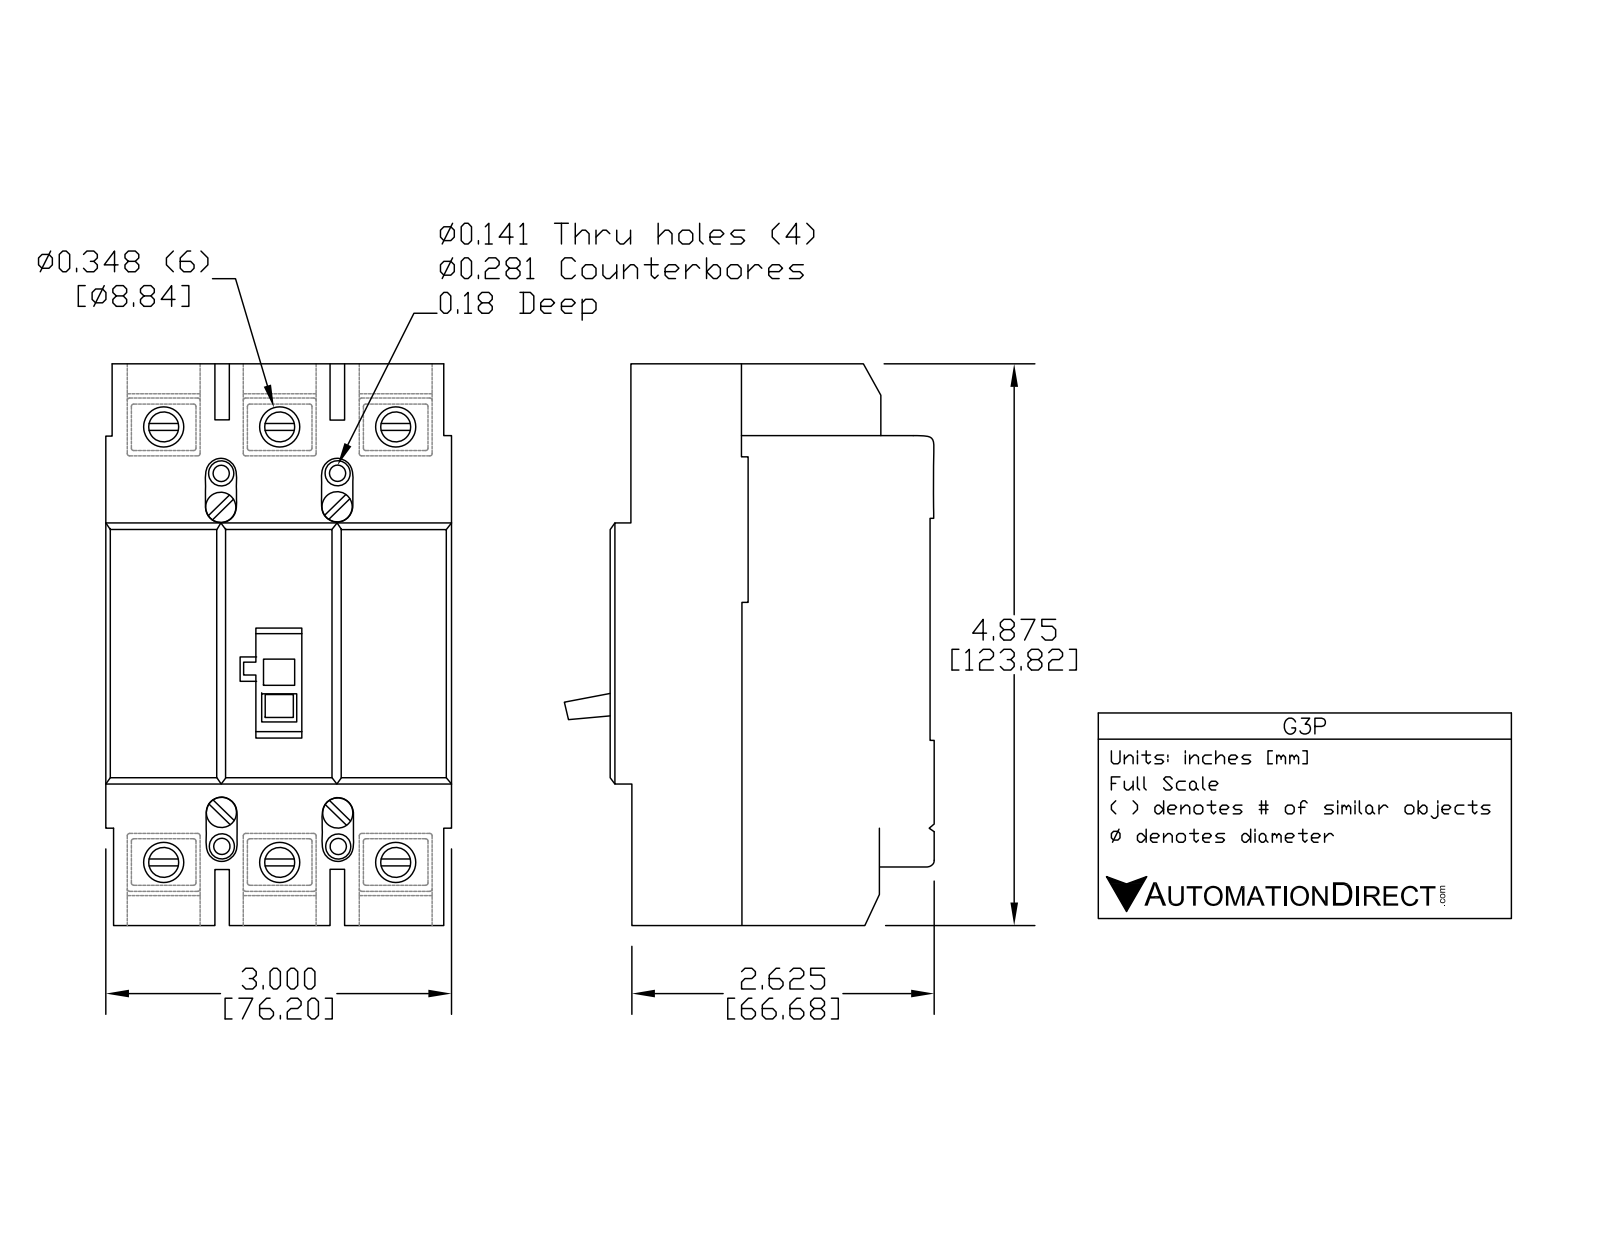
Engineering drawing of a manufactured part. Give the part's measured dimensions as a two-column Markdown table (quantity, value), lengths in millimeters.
| quantity | value |
| --- | --- |
| part name | G3P-090 |
| STEP written by | SolidWorks 2013 (AUTOMOTIVE_DESIGN) |
| units | millimeters |
| bodies | 16 solids, 915 faces (694 planar, 149 cylindrical, 72 other) |
| overall size | 123.83 × 82.08 × 76.08 |
| volume | 371 744 mm³ |
| surface area | 119 511 mm² |
| round holes (diameter × count) | 4 × 8, 9 × 8, 2.75 × 4, 3 × 4, 3.75 × 4, 4.75 × 2 |
| round bosses / shafts (diameter × count) | 5.4 × 8, 8 × 6, 10 × 3, 56 × 1 |
| partial cylindrical surfaces (radius × count) | 1 × 12, 3.5 × 8, 3 × 4, 2.38 × 2, 4.9 × 2, 28 × 2, 2 × 1 |
| main face-to-face distances | 25.46, 76, 23.5, 42.5, 16, 33.3, 42.7, 4.54, 24, 3 |
| hole center spacings | 7, 25.38, 8.1, 42.53, 52.53, 74.75, 79.27, 86.19 |
